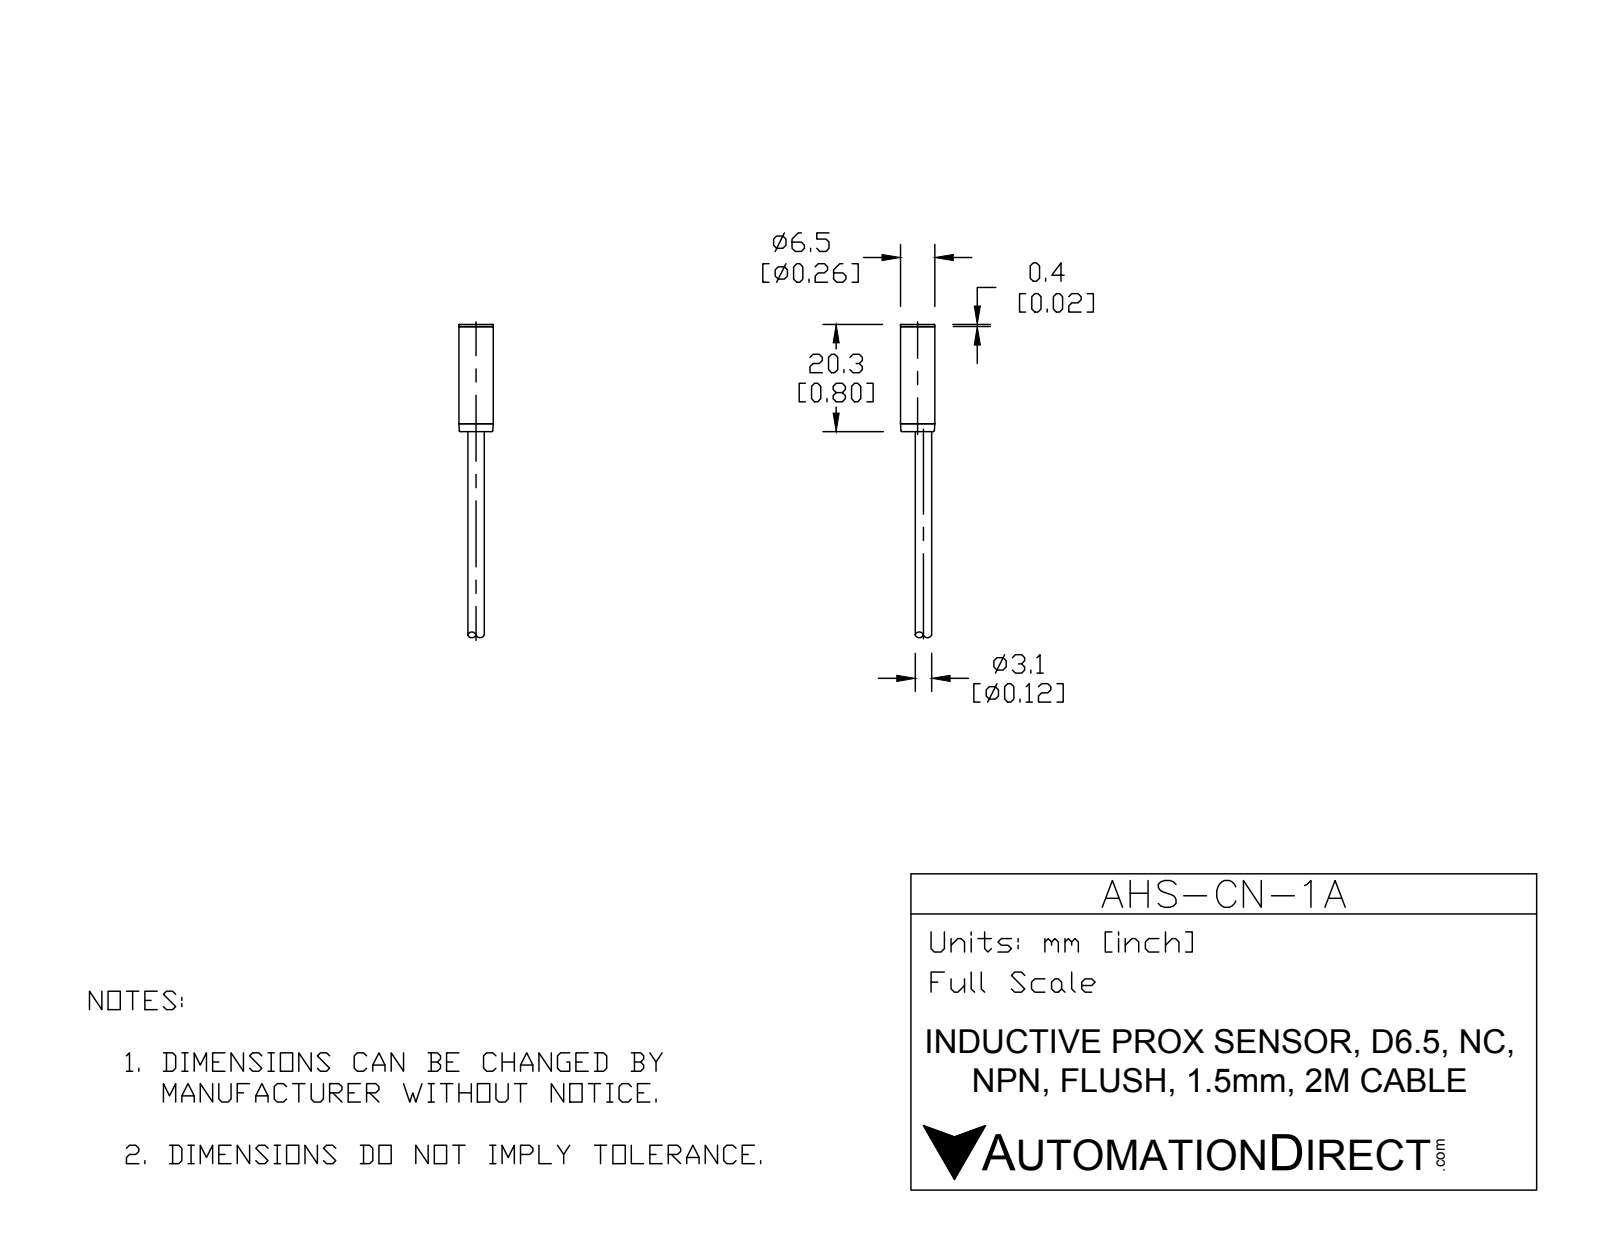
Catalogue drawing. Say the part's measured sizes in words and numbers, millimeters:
The part is named "AHS-CN-1A". Its 3-D file was written by "SolidWorks 2015 (CONFIG_CONTROL_DESIGN)". It is 2 solids with 17 faces: 5 planar, 6 cylindrical and 6 other. Overall it measures 70.3 by 6.5 by 6.5 millimeters. Its volume is 1 050 cubic millimeters and its surface area 979 square millimeters. Round bosses or shafts: 1 of diameter 6.5, 1 of diameter 3.1. The main face-to-face distances are 20.3, 50, 70.3, 69.9, 19.9, 0.4.
